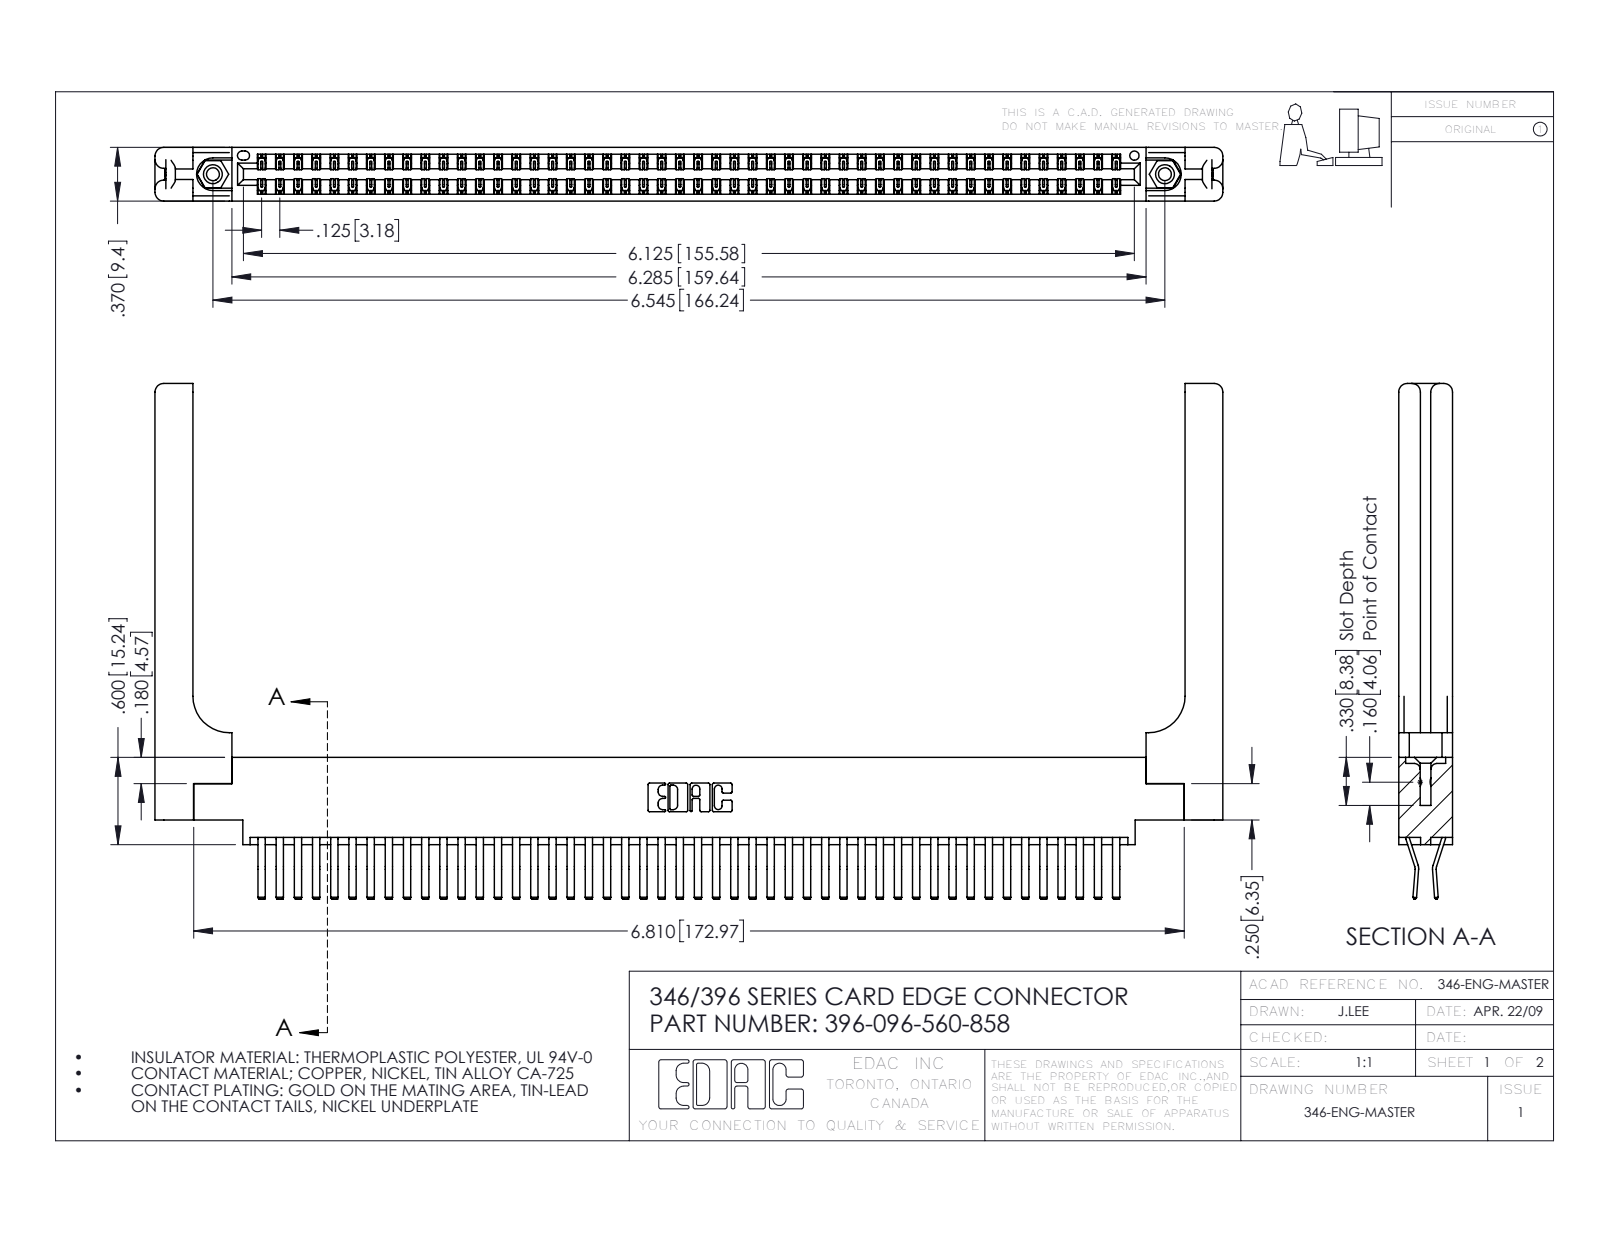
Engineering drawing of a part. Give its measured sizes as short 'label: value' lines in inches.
name: 396-096-560-858; 345-292-001_560 Tail; 346-220-058_345-220-058; 346 Part_0.170 Offset - 0.156 Dia-TH (+1 more)
written by: SolidWorks 2016 (CONFIG_CONTROL_DESIGN)
unit: in
bodies: 101 solids, 5566 faces (3588 planar, 1918 cylindrical, 60 other)
size: 7.341 × 3.545 × 0.37
volume: 1.599 in³; area: 50.58 in²
holes: 2× ⌀0.089, 2× ⌀0.125, 2× ⌀0.156, 1× ⌀0.064
bosses: 2× ⌀0.155
rounds: 144× R0.006, 22× R0.01, 16× R0.06, 6× R0.007, 6× R0.031, 3× R0.026, 2× R0.01, 2× R0.014
face distances: 0.37, 0.048, 0.322, 0.072, 0.025, 0.148, 0.15, 0.25, 0.298, 0.275
hole spacings: 0.246, 6.336, 6.545
